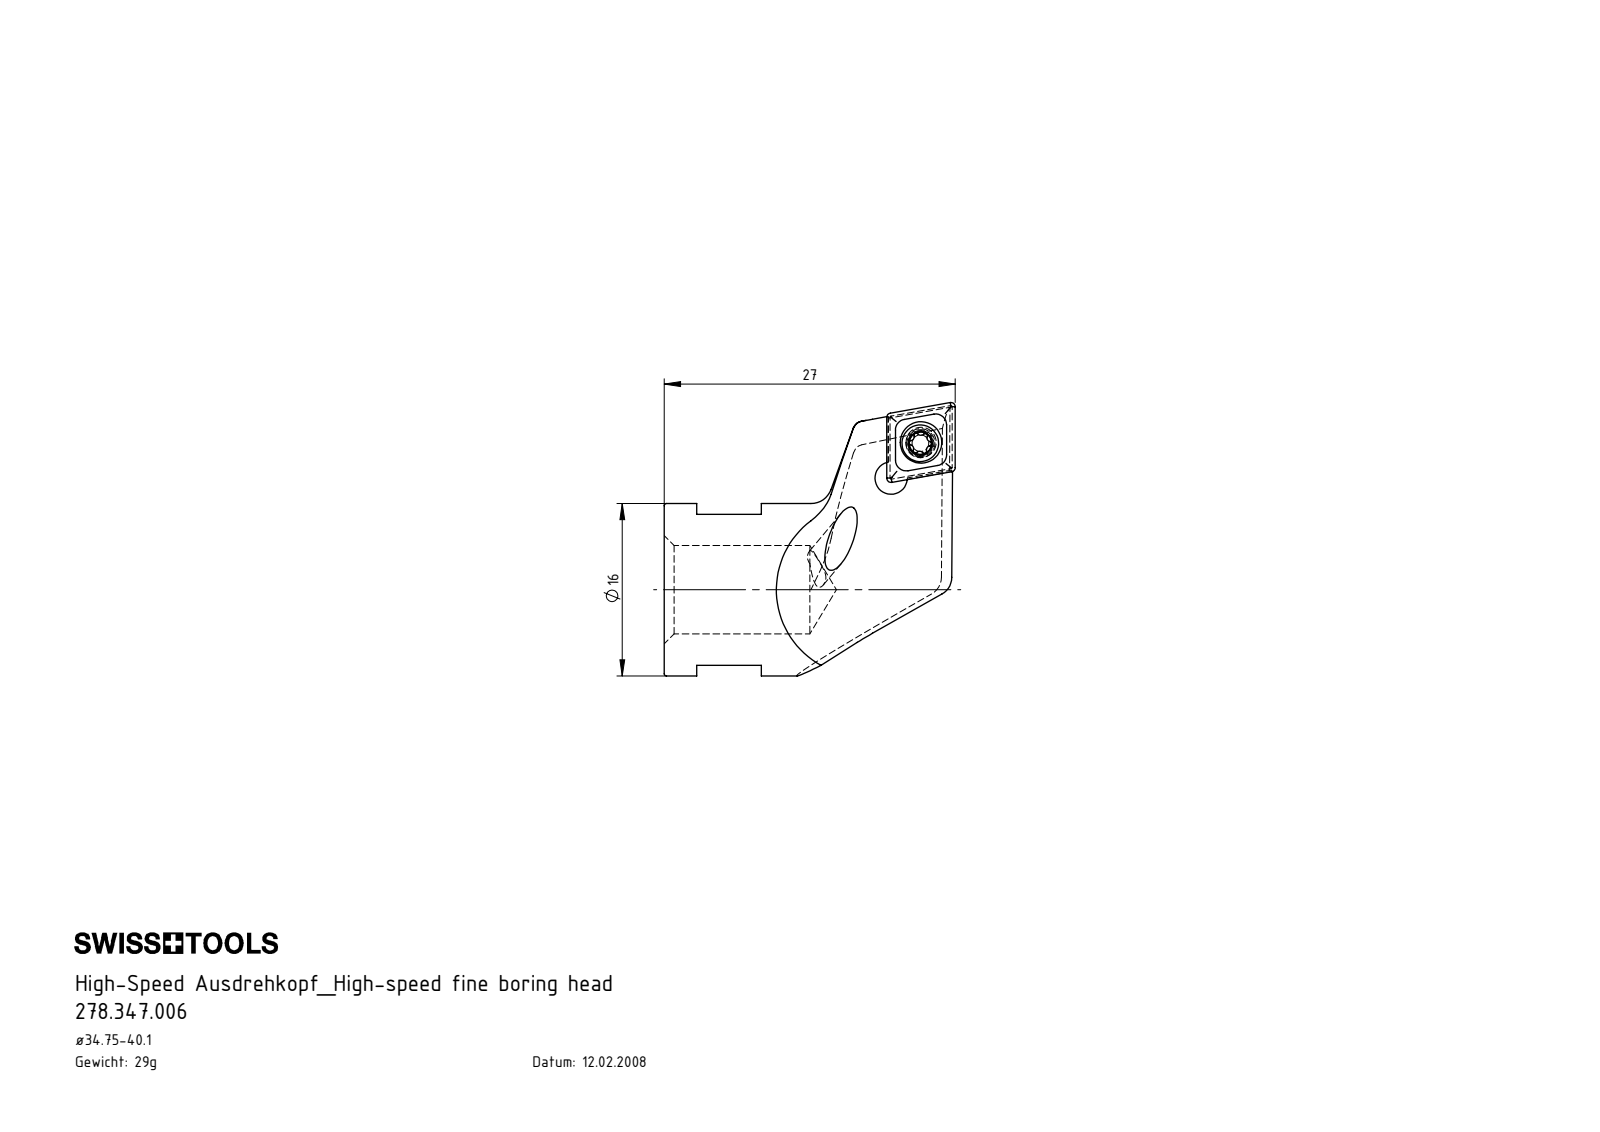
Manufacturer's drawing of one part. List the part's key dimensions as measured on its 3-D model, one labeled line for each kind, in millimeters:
Part name (STEP PRODUCT): WCA-ER2.001.006_A; HS0-A35.K11.027_A; CCMT060204; HS0-A35.K11.027
STEP written by: SolidWorks 2015 (CONFIG_CONTROL_DESIGN)
Units: millimetres
Bodies: 3 solids, 133 faces (39 planar, 40 cylindrical, 54 other)
Overall size (bounding box): 27 × 25.38 × 16
Volume: 3 691 mm³ · Surface area: 2 372 mm²
Round holes (diameter × count): ⌀2.05 ×1, ⌀2.8 ×1, ⌀3 ×1, ⌀3.85 ×1, ⌀8.2 ×1
Round bosses / shafts (diameter × count): ⌀16 ×1, ⌀3.4 ×1, ⌀2.5 ×1
Partial cylindrical surfaces — rounded edges, fillets, slot ends (radius × count): R0.21 ×6, R0.36 ×5, R1 ×4, R0.36 ×1, R1.5 ×1, R1.8 ×1, R2 ×1
Main face-to-face distances: 7.9, 5.62, 2.28, 14, 6, 8, 2.38, 9, 3, 5.42
